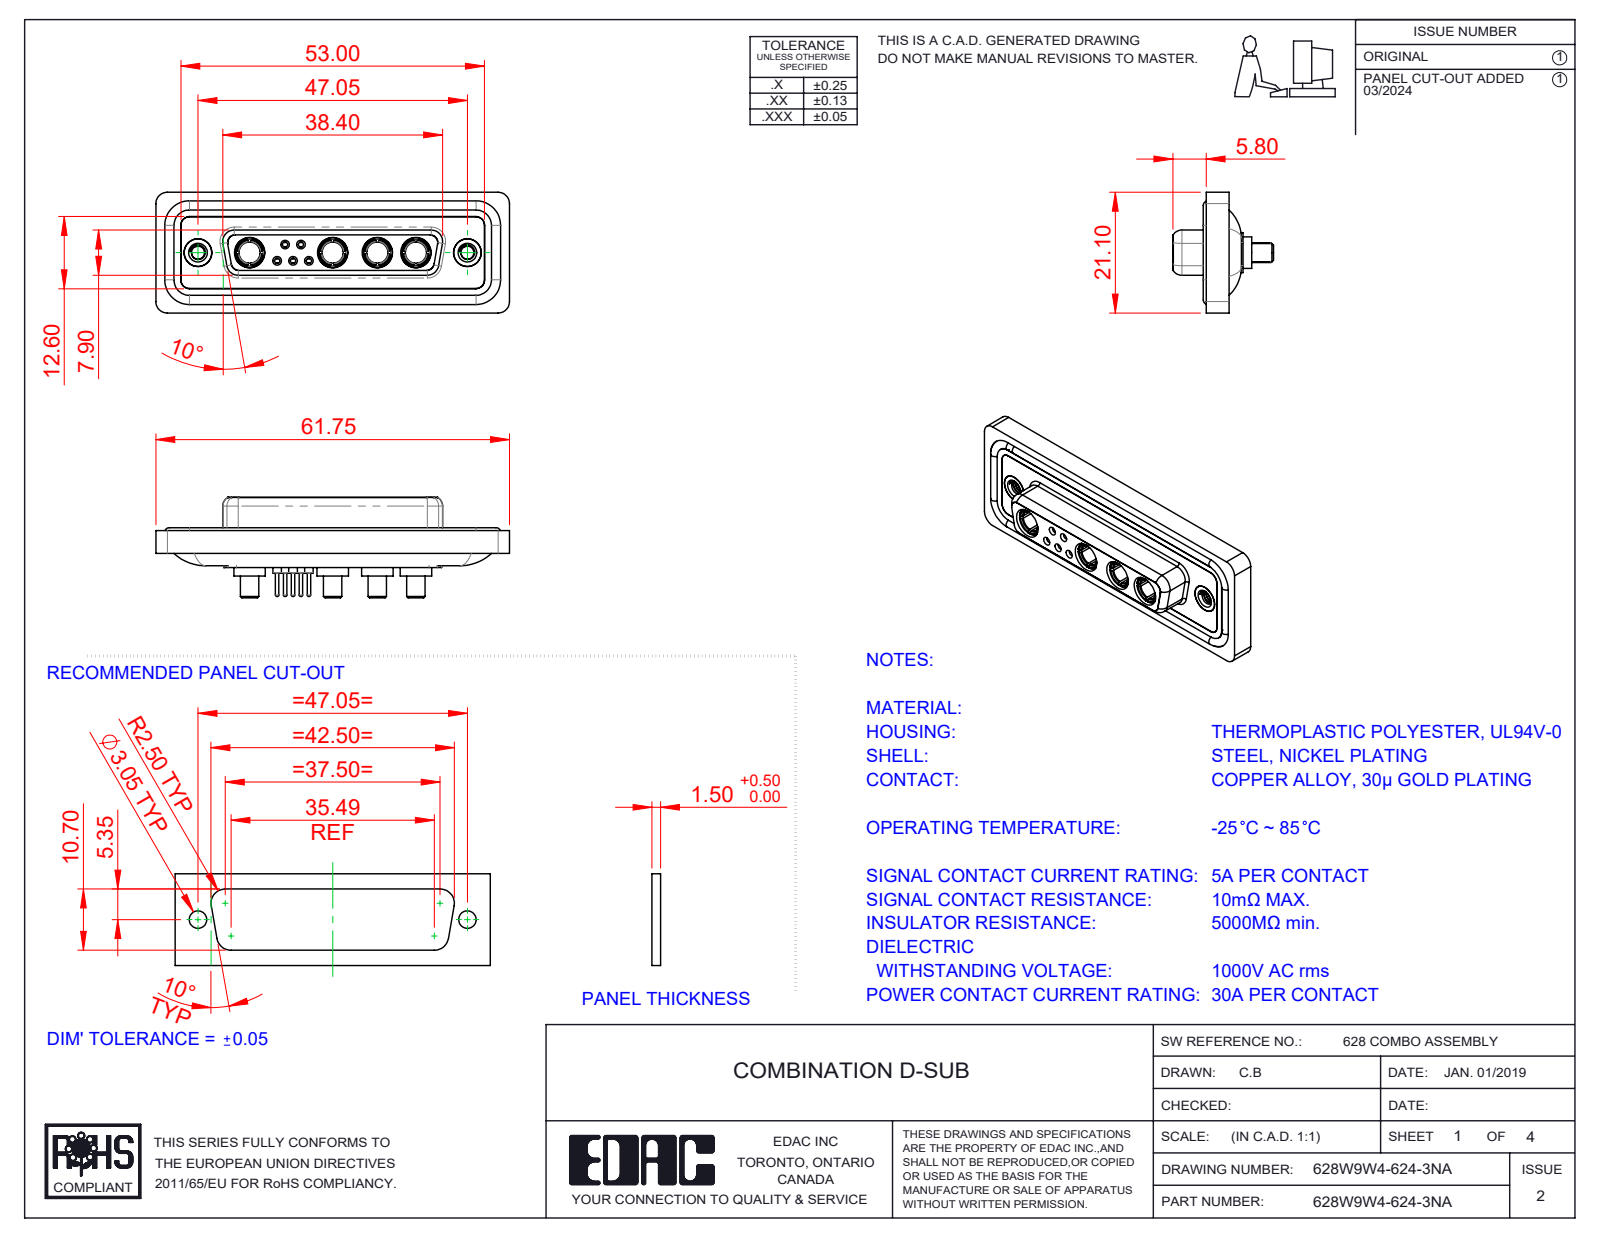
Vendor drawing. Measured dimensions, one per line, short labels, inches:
name: 628Combo Waterproof Housing_25 Contacts; 628Combo Contact Row 1_24; 628Combo Contact Row 2_24; 628Combo Housing_9W4 (+5 more)
written by: SolidWorks 2023 (CONFIG_CONTROL_DESIGN)
unit: in
bodies: 20 solids, 955 faces (296 planar, 377 cylindrical, 282 other)
size: 2.431 × 0.831 × 0.691
volume: 0.504 in³; area: 21.05 in²
holes: 6× ⌀0.191, 5× ⌀0.035, 5× ⌀0.043, 5× ⌀0.059, 5× ⌀0.079, 4× ⌀0.146, 4× ⌀0.209, 3× ⌀0.063, 2× ⌀0.067, 2× ⌀0.089, 2× ⌀0.157, 2× ⌀0.159
bosses: 6× ⌀0.063, 5× ⌀0.087, 5× ⌀0.024, 4× ⌀0.217, 4× ⌀0.205, 4× ⌀0.195, 4× ⌀0.187, 4× ⌀0.148
rounds: 22× R0.059, 18× R0.079, 8× R0.053, 8× R0.063, 4× R0.01, 4× R0.02, 4× R0.024, 4× R0.026
face distances: 0.016, 0.071, 0.293, 0.222, 0.02, 0.278, 0.26, 0.063, 0.043, 0.114
hole spacings: 0.124, 0.109, 0.198, 0.109, 0.173, 0.198, 0.218, 0.226
